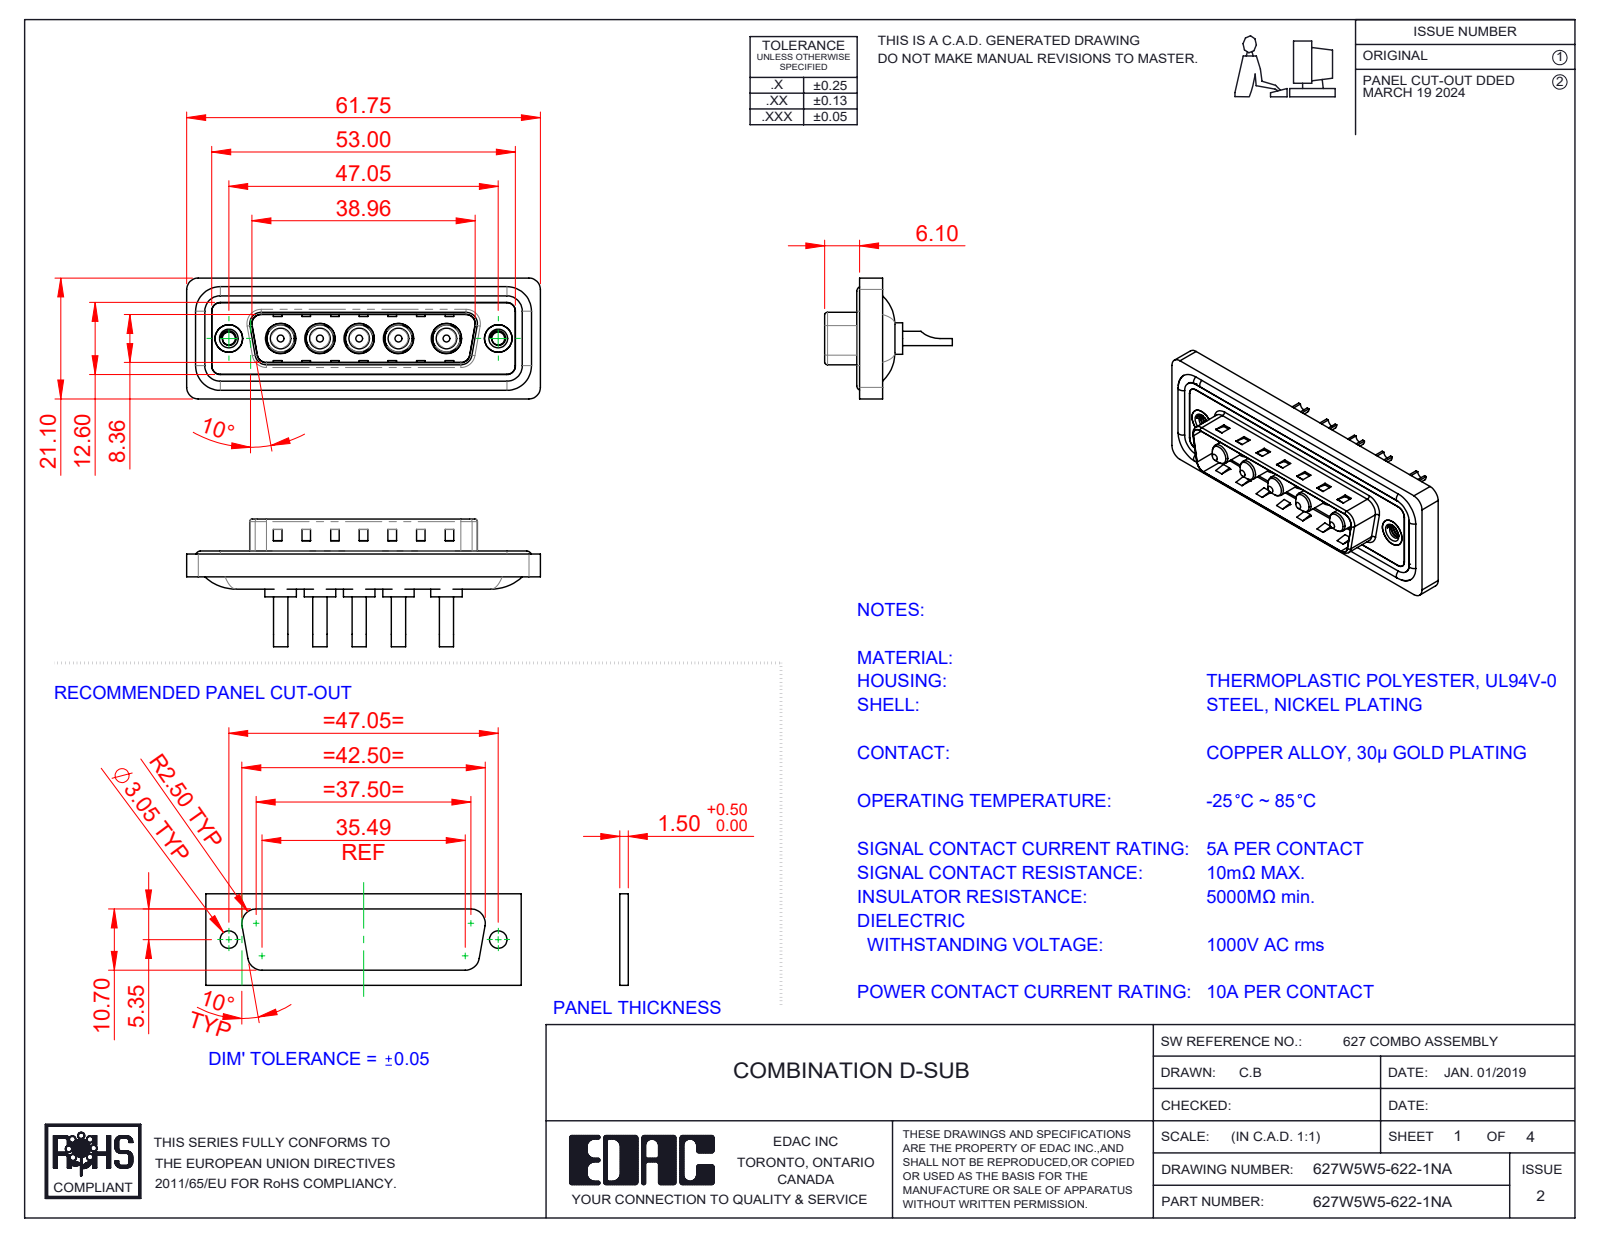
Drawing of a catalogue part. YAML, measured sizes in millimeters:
part_name: "627Combo Housing_5W5; 627W5W5-622-1NA; 627Combo Waterproof Housing_25 Contacts; 627Combo Shell Rear_25 Contacts (+3 more)"
step_written_by: "SolidWorks 2023 (CONFIG_CONTROL_DESIGN)"
units: millimeters
bodies: {solids: 17, faces: 706, planar: 269, cylindrical: 300, other: 137}
overall_size: [61.75, 22.3, 21.1]
volume: 7461
surface_area: 12032
round_holes:
  - {diameter: 1.7, count: 5}
  - {diameter: 4.85, count: 5}
  - {diameter: 5.3, count: 5}
  - {diameter: 2.26, count: 2}
  - {diameter: 4, count: 2}
  - {diameter: 4.8, count: 2}
  - {diameter: 5, count: 2}
round_bosses_or_shafts:
  - {diameter: 5.5, count: 5}
  - {diameter: 5.2, count: 5}
  - {diameter: 4.75, count: 5}
  - {diameter: 3.75, count: 5}
  - {diameter: 3.6, count: 5}
  - {diameter: 2.5, count: 5}
  - {diameter: 1.6, count: 4}
  - {diameter: 4.9, count: 2}
partial_cylinders:
  - {radius: 1.5, count: 22}
  - {radius: 2, count: 18}
  - {radius: 0.5, count: 8}
  - {radius: 1.6, count: 8}
  - {radius: 2.1, count: 5}
  - {radius: 0.25, count: 4}
  - {radius: 0.6, count: 4}
  - {radius: 0.65, count: 4}
face_to_face_distances: [0.4, 1.5, 0.5, 1.1, 3.1, 1.6, 2.9, 0.82, 9.58, 5.65]
hole_center_spacings: [6.86, 9.04, 13.73, 38.01, 6.87, 8.37, 8.38, 9.05]
